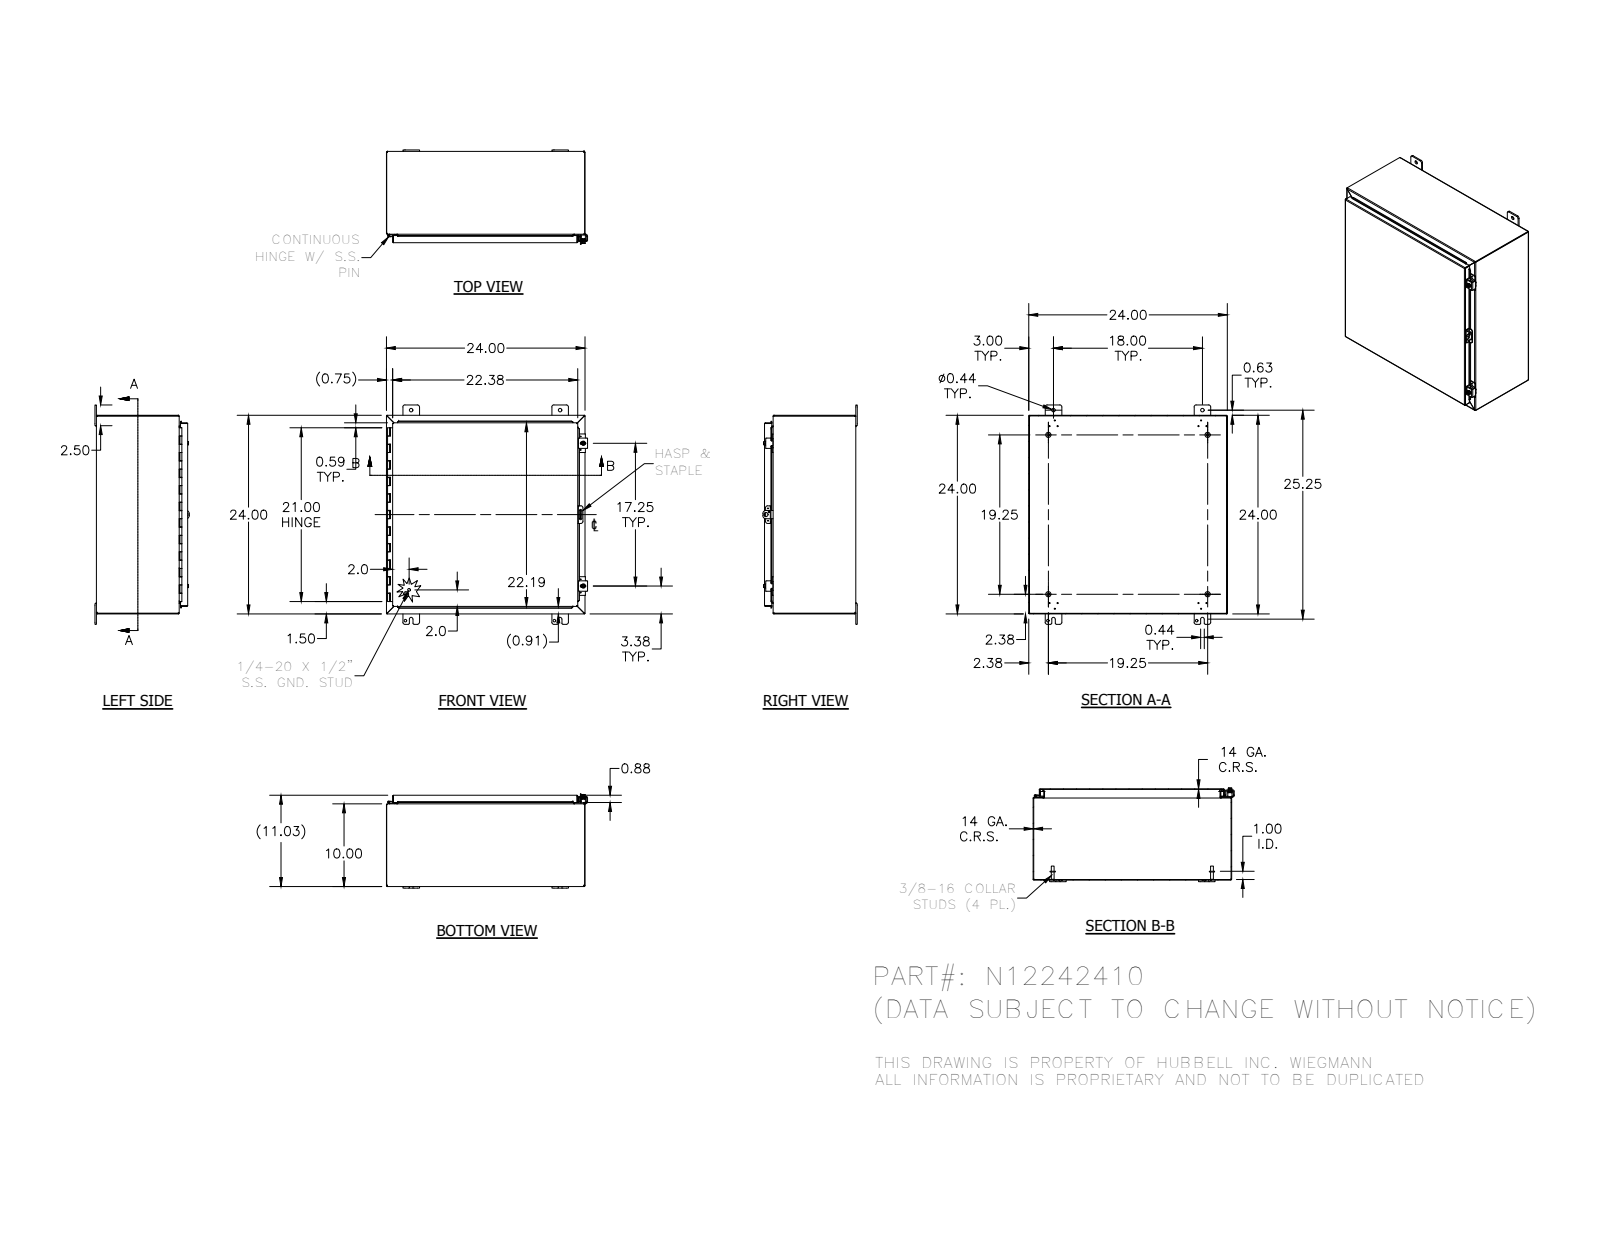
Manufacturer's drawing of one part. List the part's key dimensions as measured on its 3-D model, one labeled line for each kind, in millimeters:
Part name (STEP PRODUCT): N12242410; 34840; 38420; N12242410BKP (+8 more)
STEP written by: Autodesk Inventor 2012 (AUTOMOTIVE_DESIGN)
Units: millimetres
Bodies: 27 solids, 982 faces (533 planar, 332 cylindrical, 117 other)
Overall size (bounding box): 673.1 × 617.5 × 289.8
Volume: 3 074 000 mm³ · Surface area: 3 171 000 mm²
Round holes (diameter × count): ⌀3 ×12, ⌀2.8 ×7, ⌀8 ×4, ⌀11.1 ×4, ⌀5.4 ×2, ⌀7.1 ×2, ⌀7.6 ×2, ⌀3.2 ×1, ⌀4 ×1, ⌀12.7 ×1
Round bosses / shafts (diameter × count): ⌀15.9 ×4, ⌀8.4 ×4, ⌀6.4 ×4, ⌀13.2 ×2, ⌀12.7 ×2, ⌀8.9 ×2, ⌀2.9 ×2, ⌀8.6 ×1
Partial cylindrical surfaces — rounded edges, fillets, slot ends (radius × count): R0.8 ×27, R1.6 ×25, R3.2 ×25, R6.4 ×25, R0.8 ×23, R2.7 ×23, R1.8 ×8, R2.5 ×4
Main face-to-face distances: 1.9, 278.4, 607.7, 276.5, 280.2, 609.6, 605.8, 252.1, 26.2, 254
Hole centre spacings: 457.2, 19.3, 23.9, 24.6, 50.7, 441.2, 465.8, 543.1
